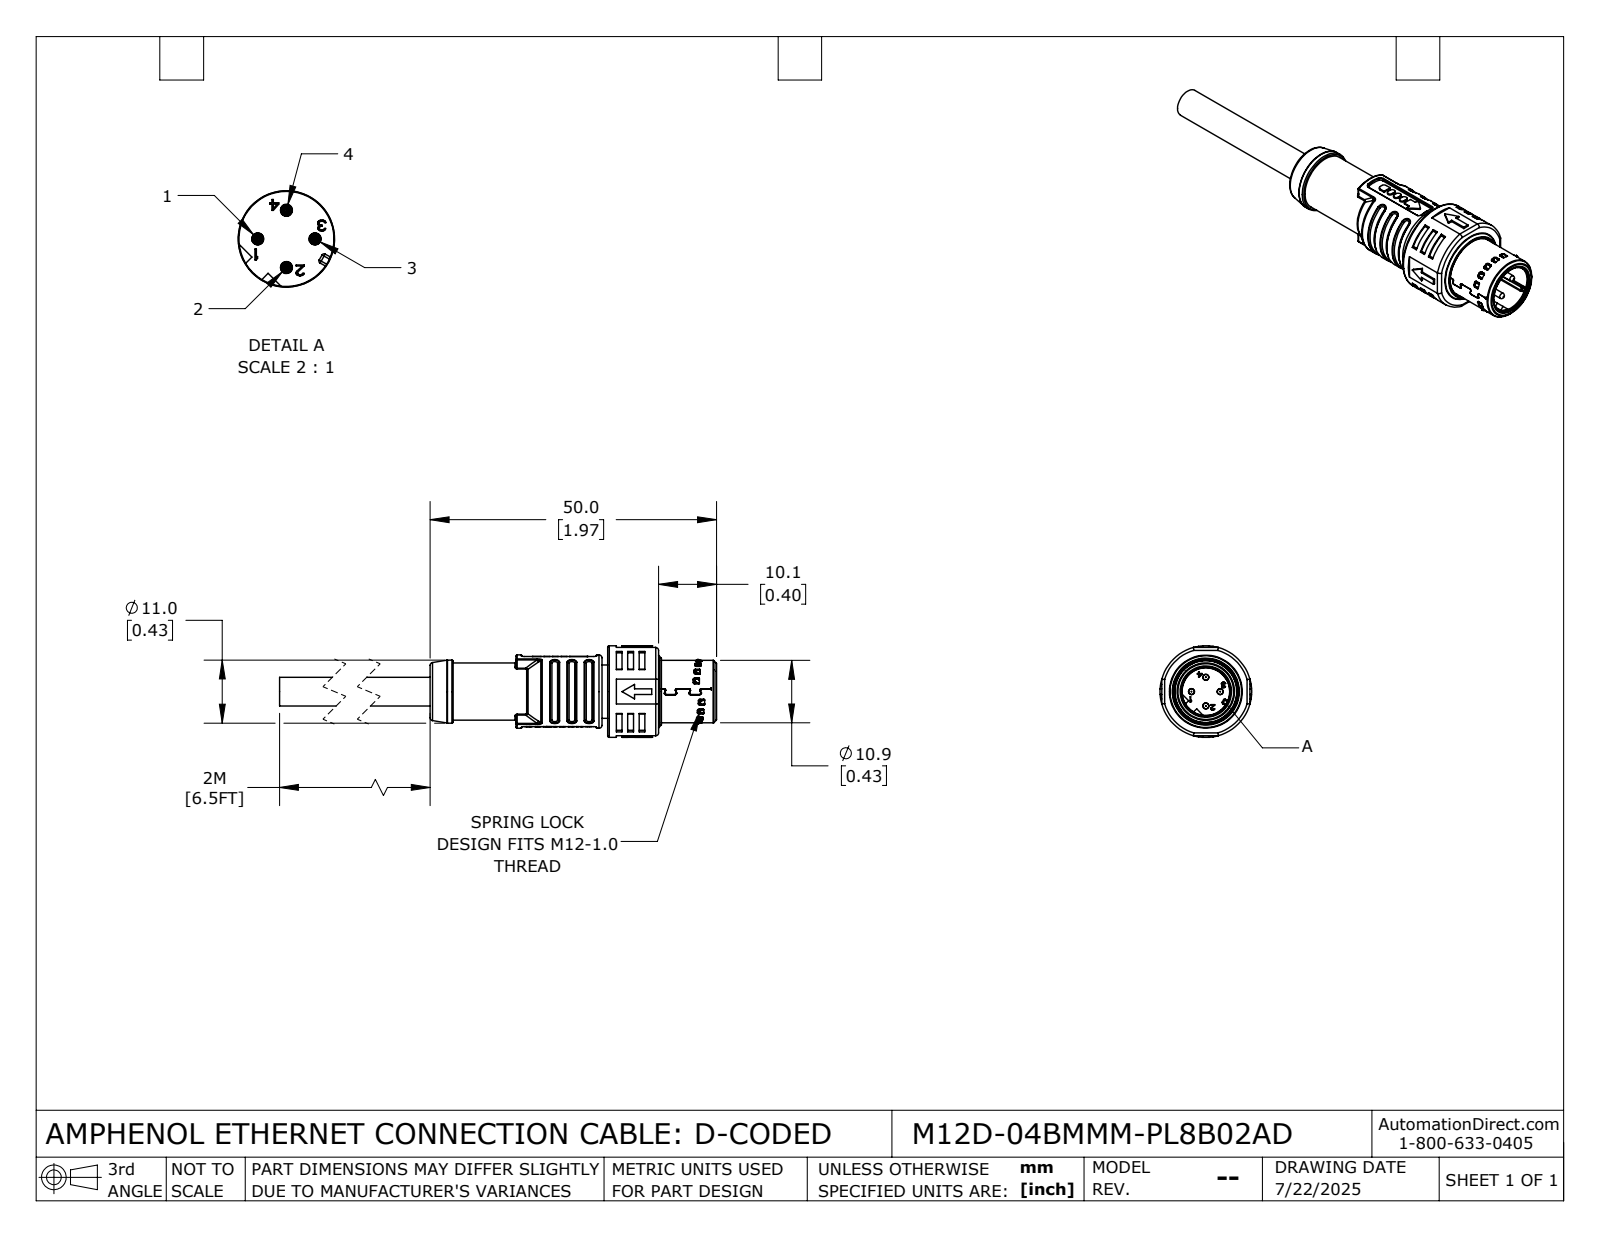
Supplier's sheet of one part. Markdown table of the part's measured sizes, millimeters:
| quantity | value |
| --- | --- |
| part name | M12D-04BMMM-PL8B02AD |
| STEP written by | SolidWorks 2024 (CONFIG_CONTROL_DESIGN) |
| units | millimeters |
| bodies | 1 solid, 2139 faces (996 planar, 644 cylindrical, 499 other) |
| overall size | 80 × 16 × 16 |
| volume | 5 399 mm³ |
| surface area | 5 961 mm² |
| round holes (diameter × count) | 1.05 × 4, 8.3 × 1, 9 × 1, 10.15 × 1, 10.5 × 1, 10.9 × 1, 11.5 × 1, 11.8 × 1, 14.2 × 1 |
| round bosses / shafts (diameter × count) | 1 × 4, 16 × 1, 14.1 × 1, 12.8 × 1, 12.4 × 1, 11 × 1, 10.45 × 1, 10.4 × 1 |
| partial cylindrical surfaces (radius × count) | 0.2 × 119, 0.25 × 66, 0.3 × 64, 0.15 × 44, 0.5 × 38, 0.13 × 12, 0.7 × 11, 0.1 × 7 |
| main face-to-face distances | 1, 30, 10.1, 8.9, 2.5, 1.2, 8.6, 32.5, 15.4, 1.5 |
| hole center spacings | 2.5, 3.54, 5 |
